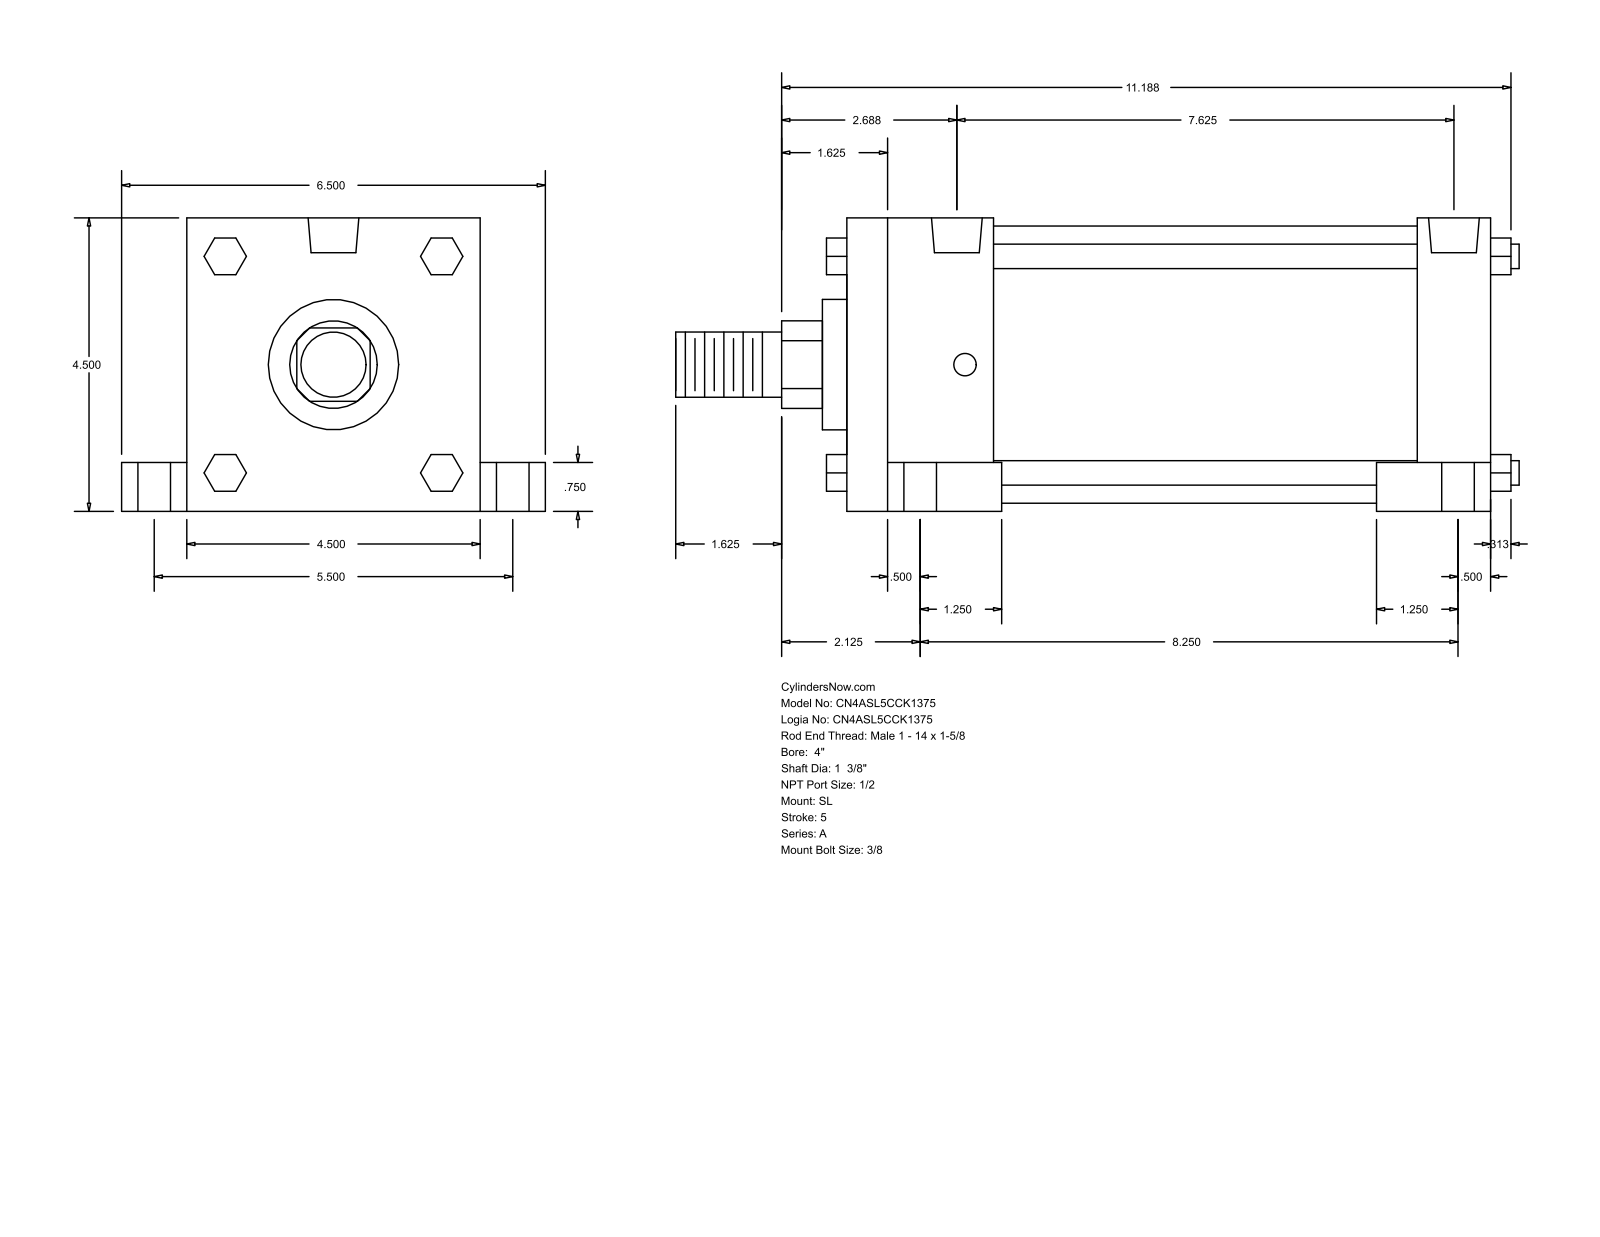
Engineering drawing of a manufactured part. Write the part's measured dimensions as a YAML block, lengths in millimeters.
part_name: "A_SL__0400_1.375"
step_written_by: "GSSL Pune (CONFIG_CONTROL_DESIGN)"
units: millimeters
bodies: {solids: 0, faces: 150, planar: 114, cylindrical: 36, other: 0}
overall_size: [328.61, 165.1, 114.3]
round_holes:
  - {diameter: 8.73, count: 4}
  - {diameter: 12.7, count: 4}
  - {diameter: 19.05, count: 4}
  - {diameter: 19.77, count: 2}
round_bosses_or_shafts:
  - {diameter: 9.53, count: 4}
  - {diameter: 107.95, count: 1}
  - {diameter: 50.8, count: 1}
  - {diameter: 34.92, count: 1}
  - {diameter: 25.4, count: 1}
partial_cylinders:
  - {radius: 17.06, count: 1}
face_to_face_distances: [114.3, 250.83, 165.1, 57.15, 28.58, 25.4, 193.68, 222.25, 139.7, 19.05]
hole_center_spacings: [3.18, 69.87, 70.01, 71.29, 72, 139.7, 187.32, 190.5]
